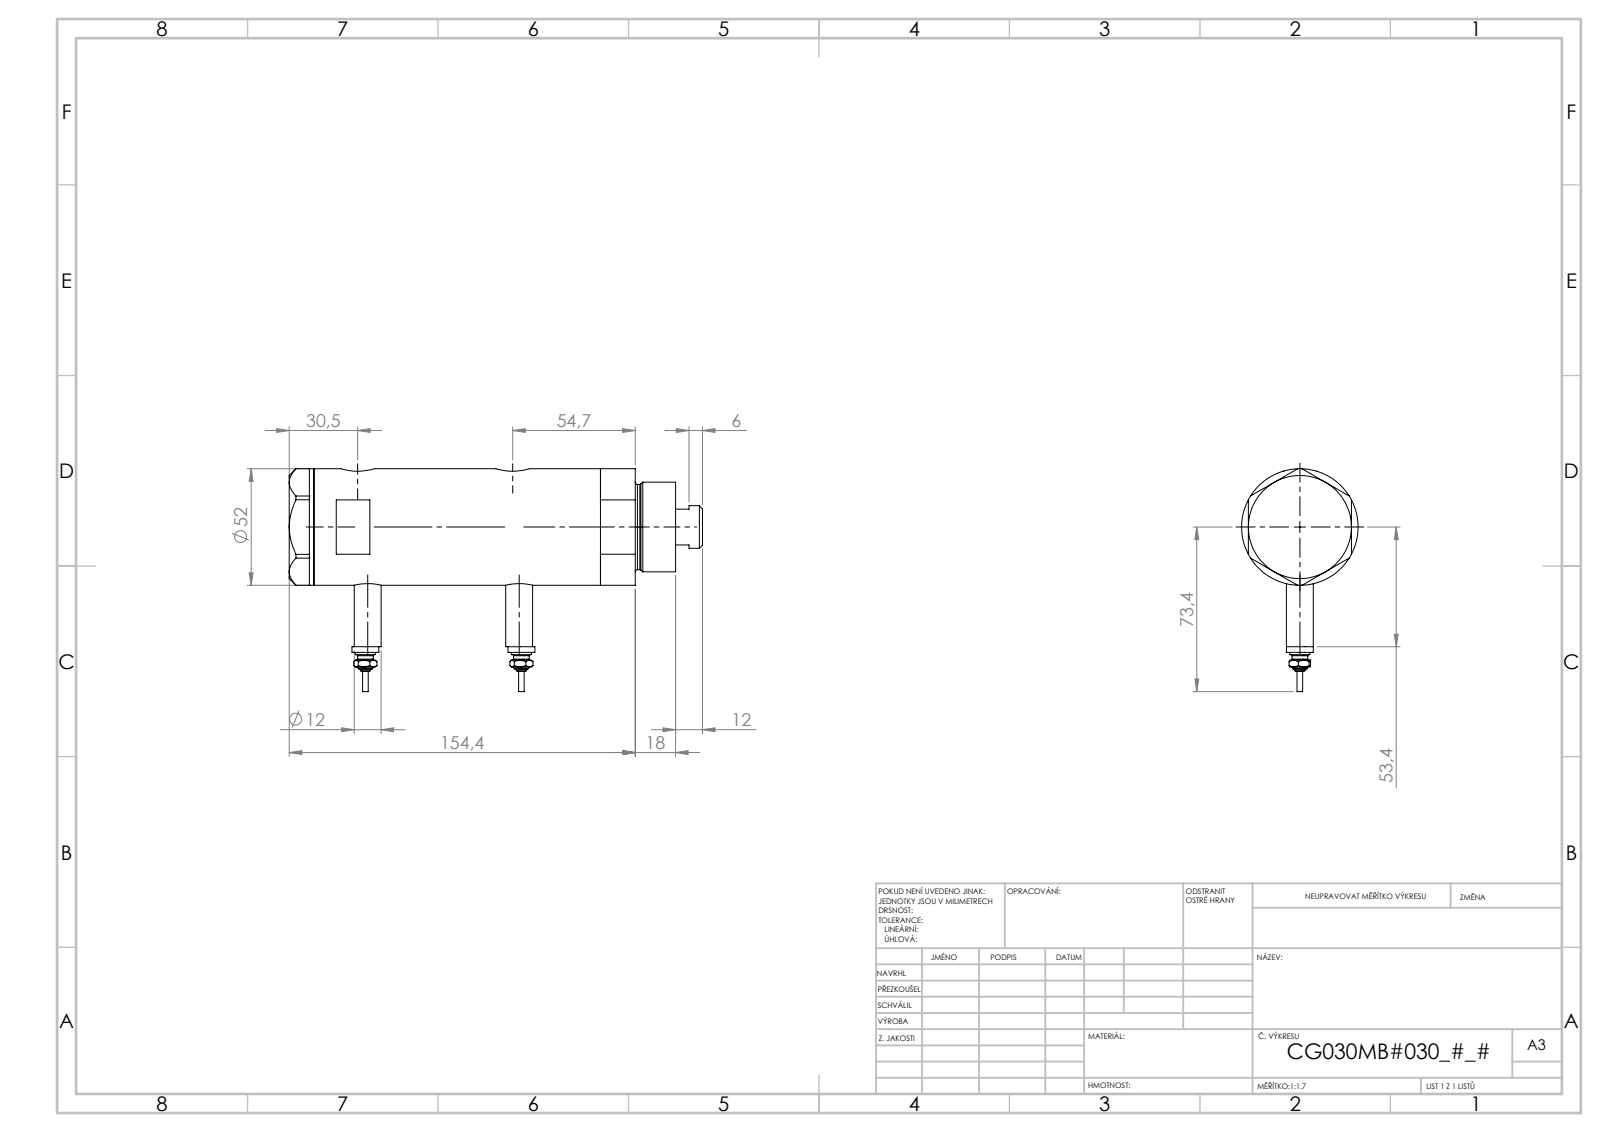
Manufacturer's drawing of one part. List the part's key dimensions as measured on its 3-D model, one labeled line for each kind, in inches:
Part name (STEP PRODUCT): V270CG_VC; V270CG_SWITCH; V270CG_BACK; V270CG_MIDDLE (+1 more)
STEP written by: SolidWorks 2019 (CONFIG_CONTROL_DESIGN)
Units: inches
Bodies: 6 solids, 246 faces (95 planar, 77 cylindrical, 74 other)
Overall size (bounding box): 7.048 × 3.319 × 2.047
Volume: 19.67 in³ · Surface area: 118.8 in²
Round holes (diameter × count): ⌀0.197 ×2, ⌀0.383 ×2, ⌀0.492 ×2, ⌀0.591 ×2, ⌀0.256 ×1, ⌀0.787 ×1, ⌀0.846 ×1, ⌀1.181 ×1, ⌀1.299 ×1, ⌀1.732 ×1
Round bosses / shafts (diameter × count): ⌀0.472 ×3, ⌀0.354 ×2, ⌀0.276 ×2, ⌀0.171 ×2, ⌀0.094 ×2, ⌀2.047 ×1, ⌀1.575 ×1, ⌀1.496 ×1
Main face-to-face distances: 0.937, 0.433, 1.37, 1.811, 3.722, 3.29, 2.352, 5.156, 4.723, 3.785
Hole centre spacings: 0.114, 0.177, 2.234, 2.348, 2.411, 2.526, 0.114, 0.115
